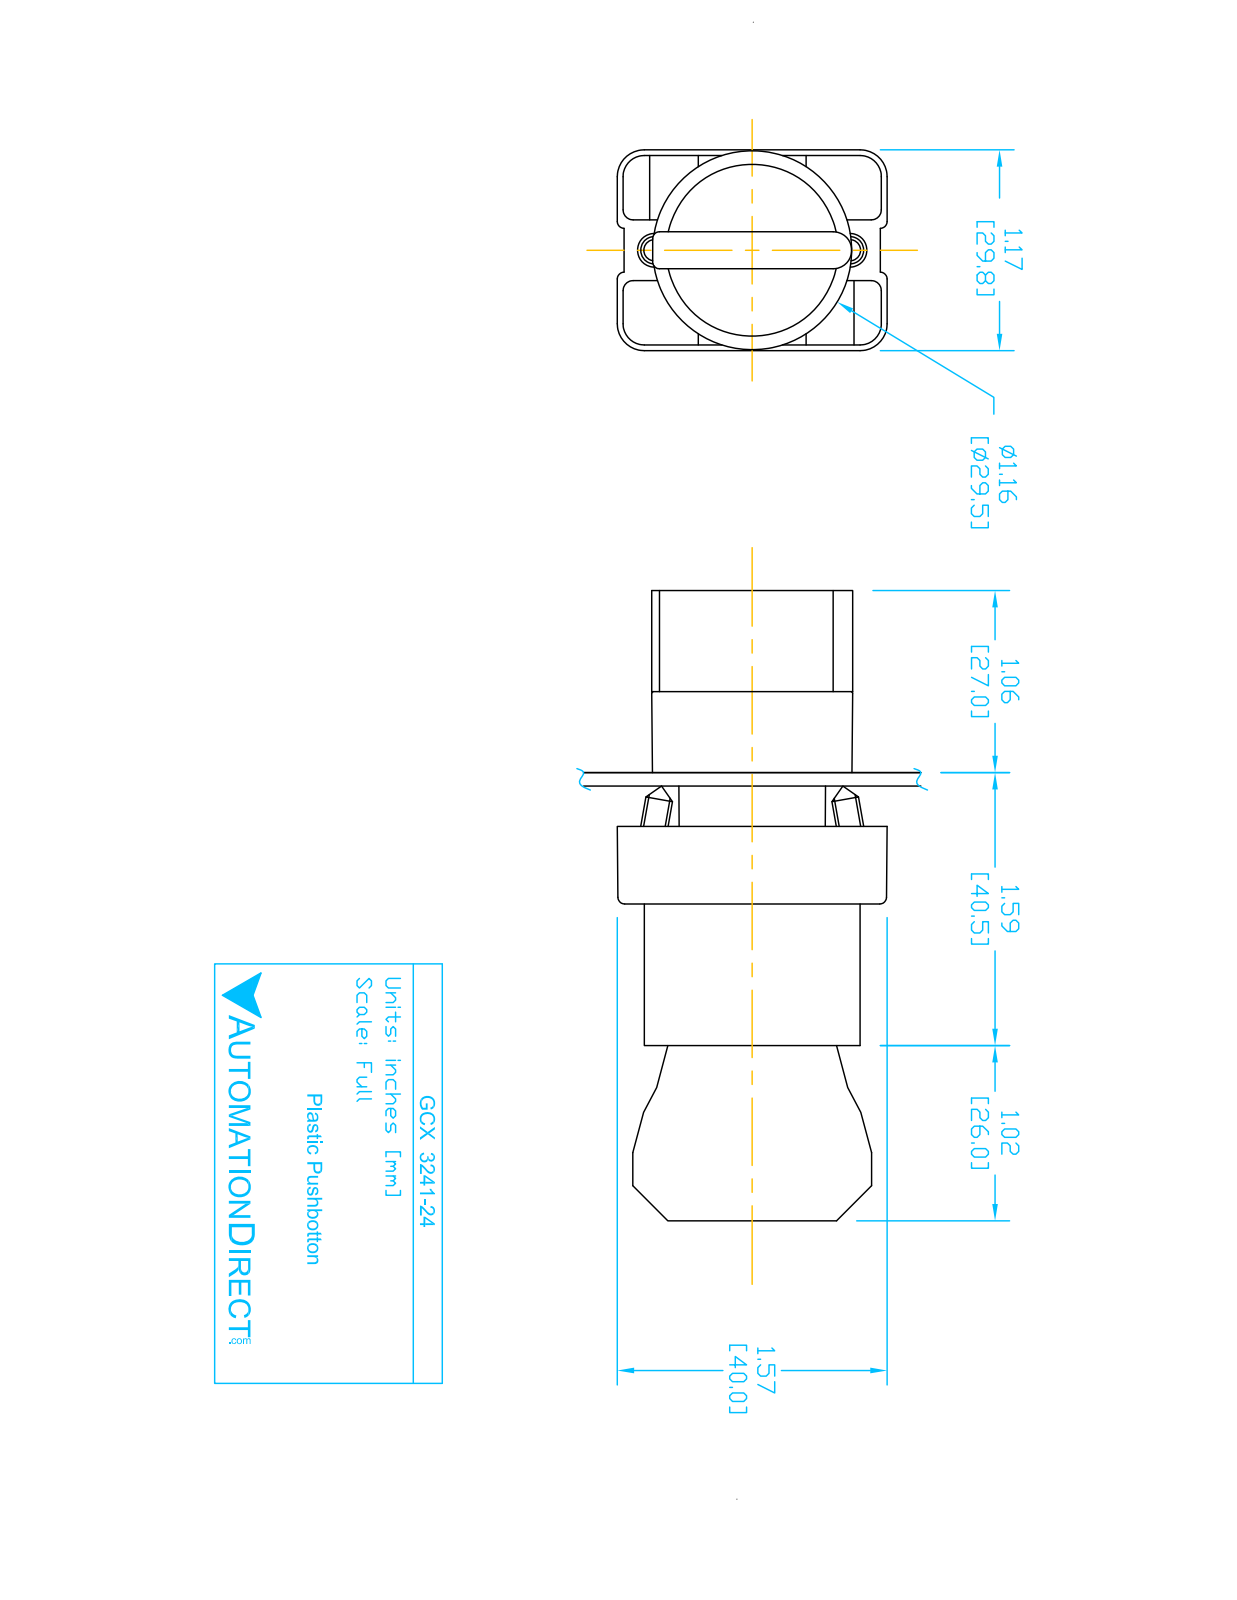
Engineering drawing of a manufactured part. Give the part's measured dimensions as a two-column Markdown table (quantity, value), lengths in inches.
| quantity | value |
| --- | --- |
| part name | ECX1050; GCX3241 OPERATOR; ecx1040; GCX3241-24 (+1 more) |
| STEP written by | SolidWorks 2016 (AUTOMOTIVE_DESIGN) |
| units | inches |
| bodies | 8 solids, 445 faces (263 planar, 151 cylindrical, 31 other) |
| overall size | 3.653 × 1.581 × 1.177 |
| volume | 2.799 in³ |
| surface area | 39 in² |
| round holes (diameter × count) | 0.079 × 2, 0.124 × 2, 0.13 × 2, 0.087 × 1, 0.197 × 1, 0.469 × 1, 0.878 × 1, 0.888 × 1, 1.024 × 1 |
| round bosses / shafts (diameter × count) | 0.157 × 4, 1.175 × 1, 1.004 × 1, 0.945 × 1, 0.856 × 1, 0.78 × 1, 0.504 × 1 |
| partial cylindrical surfaces (radius × count) | 0.059 × 24, 0.041 × 12, 0.124 × 12, 0.157 × 12, 0.039 × 9, 0.128 × 2, 0.02 × 1, 0.063 × 1 |
| main face-to-face distances | 0.827, 2.02, 1.193, 0.579, 1.244, 1.171, 0.472, 0.469, 0.031, 0.033 |
| hole center spacings | 0.236, 0.544, 0.472, 0.49 |
